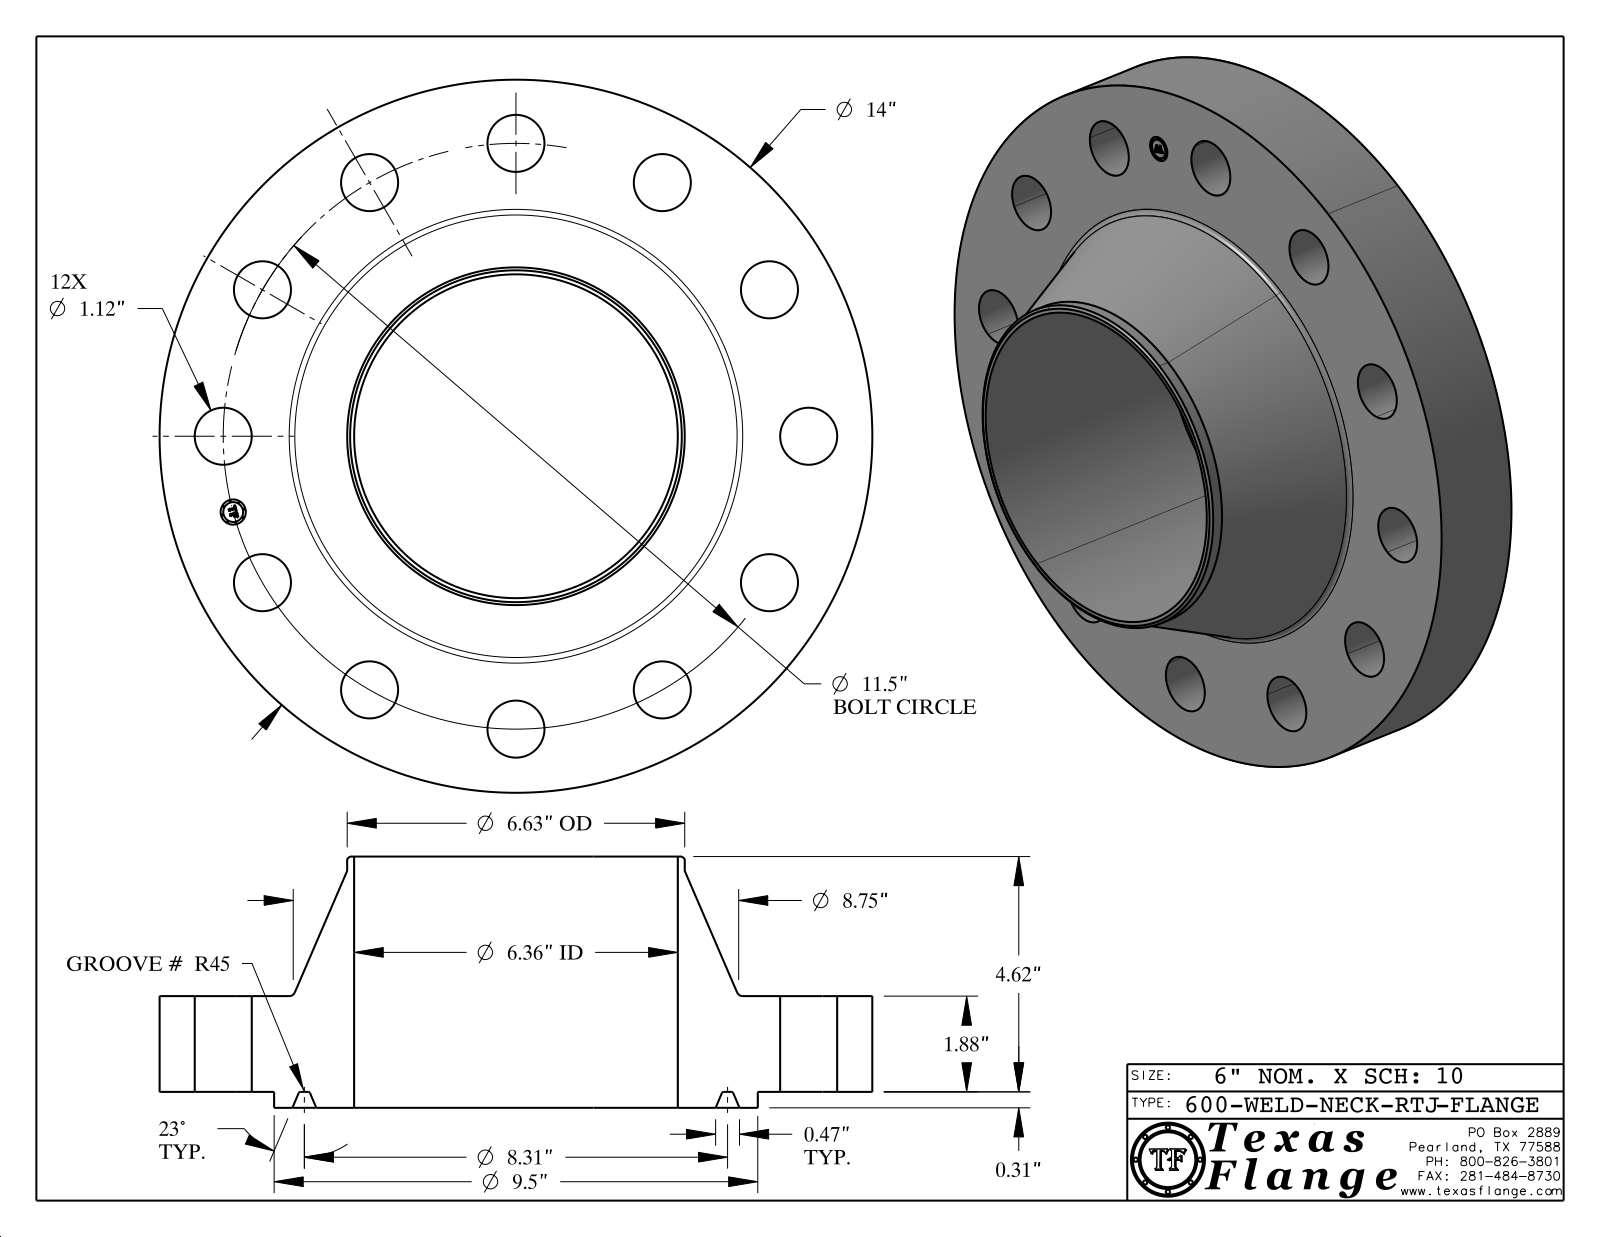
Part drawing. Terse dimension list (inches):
name: 600-WELD-NECK-RTJ
written by: CATIA V5 STEP AP214 (AUTOMOTIVE_DESIGN)
unit: in
bodies: 1 solid, 437 faces (371 planar, 52 cylindrical, 14 other)
size: 14 × 14 × 4.933
volume: 254.7 in³; area: 545.2 in²
holes: 12× ⌀1.12, 1× ⌀0.495, 1× ⌀6.357
bosses: 8× ⌀0.03, 1× ⌀14, 1× ⌀9.5, 1× ⌀6.63, 1× ⌀0.39
face distances: 1.88, 0.313, 2.193, 4.933, 4.62, 2.74, 2.178, 1.865, 0.015, 2.755
hole spacings: 5.75, 8.132, 11.108, 2.977, 5.75, 9.959, 11.5, 2.976
